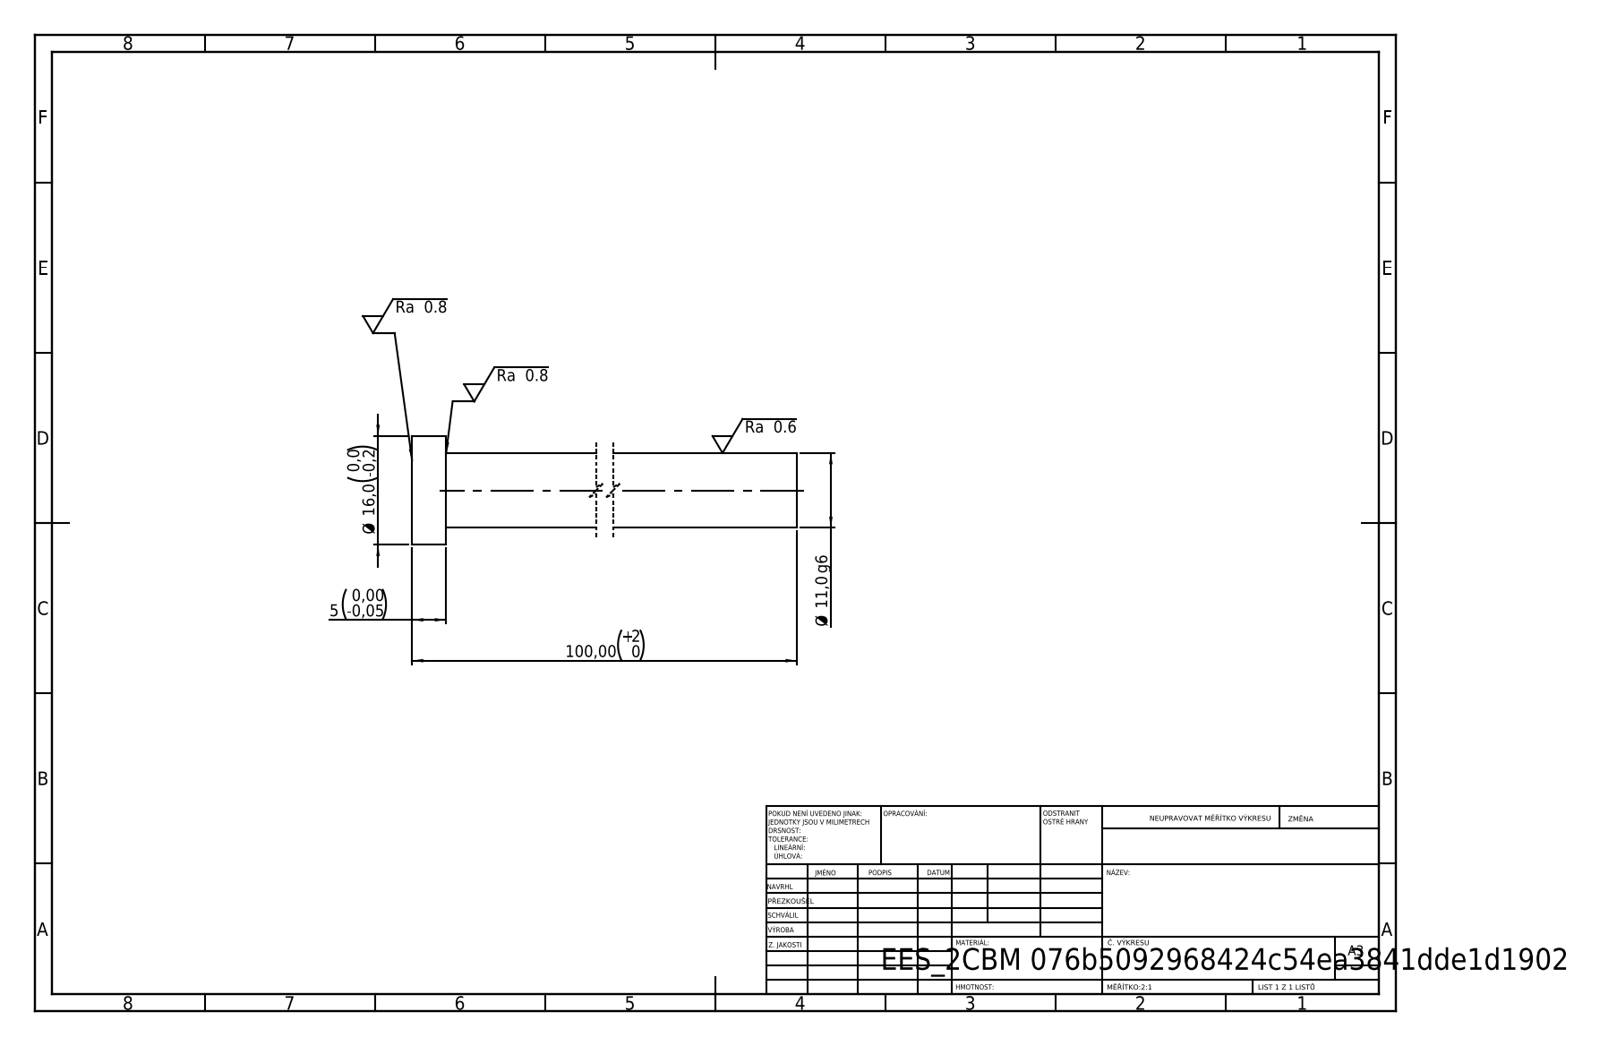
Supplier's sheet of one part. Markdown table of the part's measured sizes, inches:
| quantity | value |
| --- | --- |
| STEP written by | SolidWorks 2019 (CONFIG_CONTROL_DESIGN) |
| units | inches |
| bodies | 1 solid, 7 faces (3 planar, 4 cylindrical, 0 other) |
| overall size | 3.937 × 0.63 × 0.63 |
| volume | 0.612 in³ |
| surface area | 6.101 in² |
| round bosses / shafts (diameter × count) | 0.63 × 1, 0.433 × 1 |
| main face-to-face distances | 0.197, 3.937, 3.74 |
